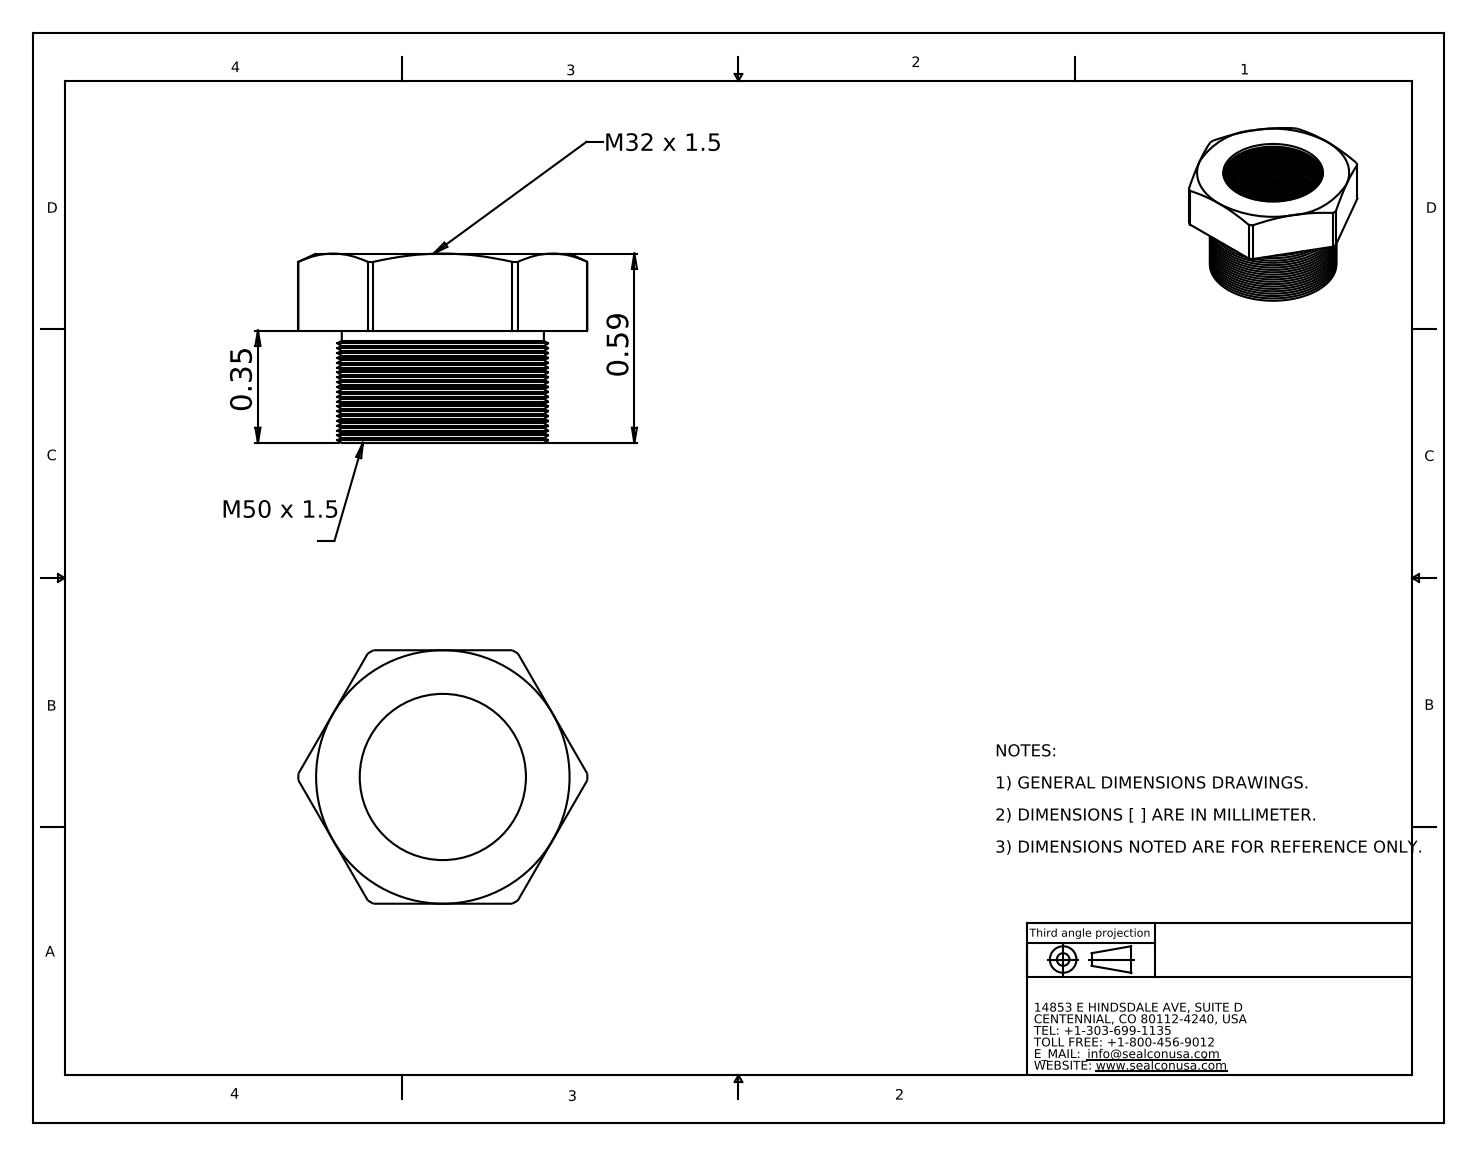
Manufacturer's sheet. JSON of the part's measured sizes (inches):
{"part_name": "RM-5032-SS", "step_written_by": "SolidWorks 2008 (CONFIG_CONTROL_DESIGN)", "units": "inches", "bodies": {"solids": 1, "faces": 329, "planar": 9, "cylindrical": 85, "other": 235}, "overall_size": [0.901, 0.79, 0.59], "volume_in3": 0.116, "surface_area_in2": 4.586, "round_holes": [[0.518, 1]], "round_bosses_or_shafts": [[0.63, 1]], "partial_cylinders_radius": [[0.45, 1]], "face_to_face_distances": [0.79, 0.24, 0.35, 0.59]}
